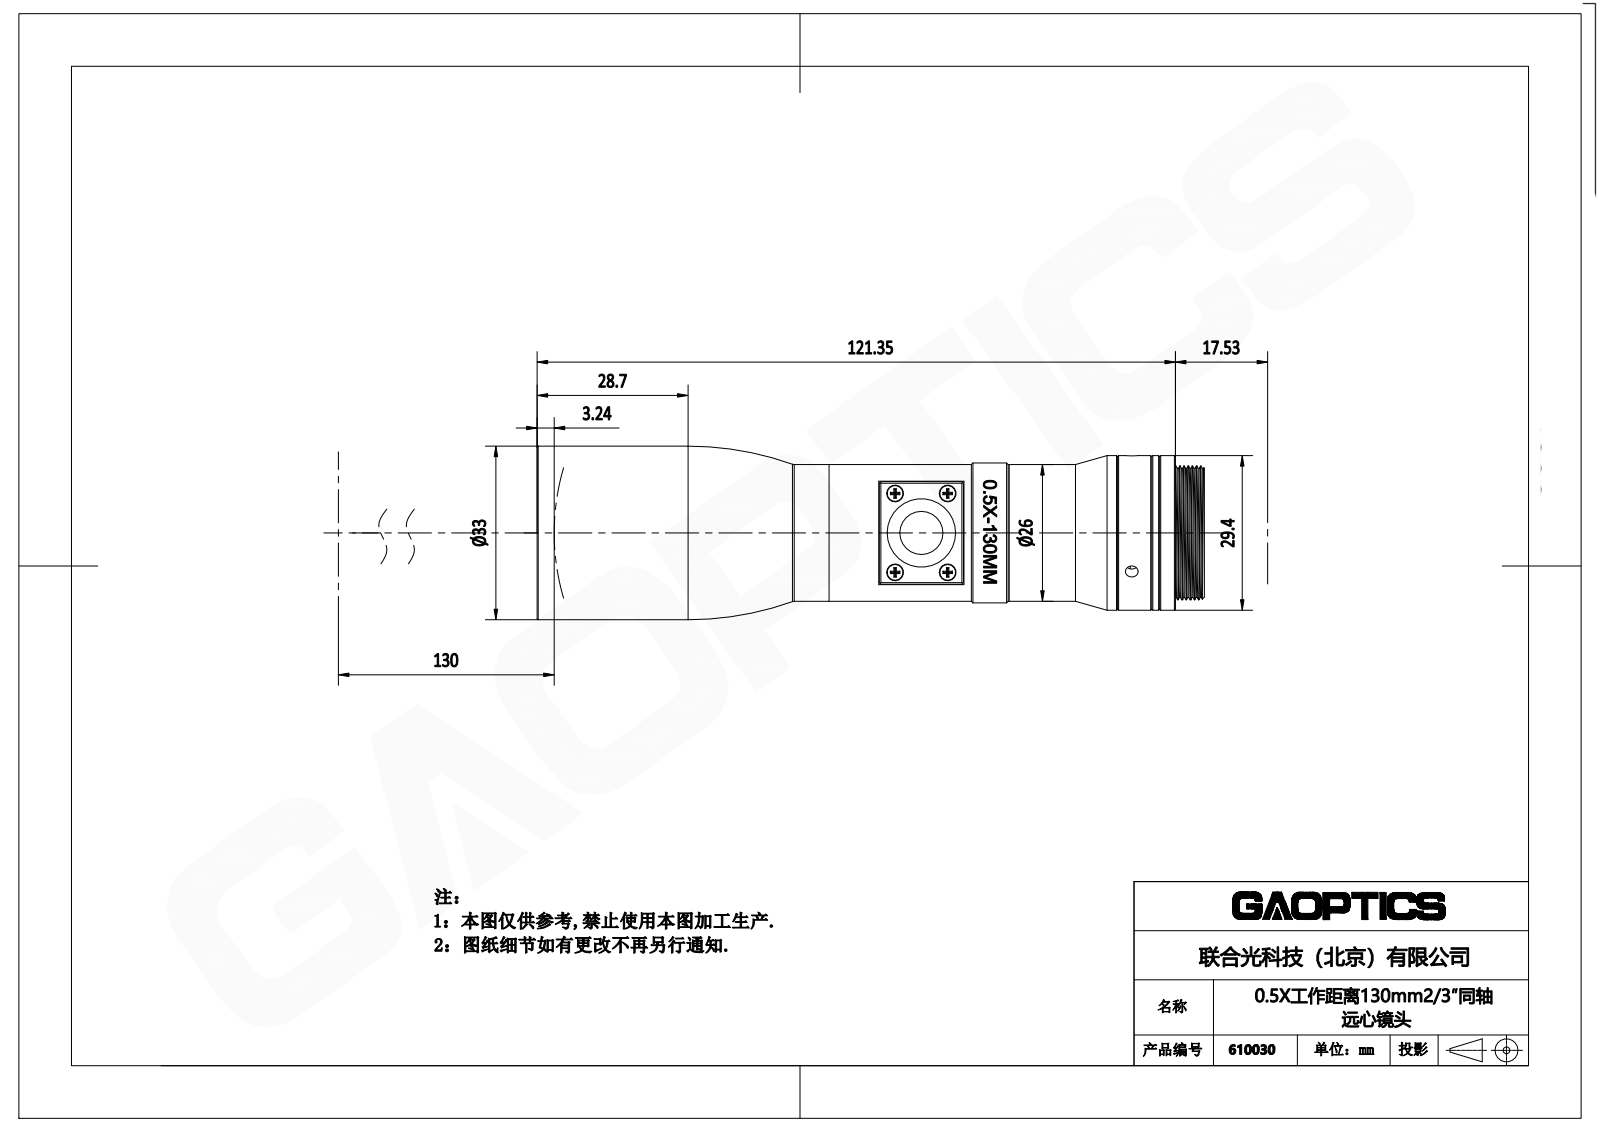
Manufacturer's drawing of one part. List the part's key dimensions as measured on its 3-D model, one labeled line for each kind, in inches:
Part name (STEP PRODUCT): 610030
STEP written by: SolidWorks 2020 (CONFIG_CONTROL_DESIGN)
Units: inches
Bodies: 18 solids, 696 faces (251 planar, 193 cylindrical, 252 other)
Overall size (bounding box): 4.967 × 1.417 × 1.299
Volume: 5.019 in³ · Surface area: 44.9 in²
Round holes (diameter × count): ⌀0.063 ×4, ⌀0.087 ×4, ⌀0.126 ×4, ⌀0.094 ×3, ⌀0.079 ×1, ⌀0.118 ×1, ⌀0.323 ×1, ⌀0.504 ×1, ⌀0.512 ×1, ⌀0.563 ×1, ⌀0.579 ×1, ⌀0.622 ×1
Round bosses / shafts (diameter × count): ⌀0.11 ×4, ⌀0.079 ×4, ⌀0.118 ×3, ⌀1.299 ×1, ⌀1.201 ×1, ⌀1.157 ×1, ⌀1.142 ×1, ⌀1.047 ×1
Partial cylindrical surfaces — rounded edges, fillets, slot ends (radius × count): R0.02 ×2, R0.522 ×1
Main face-to-face distances: 0.059, 0.118, 1.114, 0.315, 1.173, 0.858, 0.998, 0.14, 0.256, 0.116
Hole centre spacings: 0.355, 0.394, 0.418, 0.591, 0.71, 0.75, 0.492, 0.65
